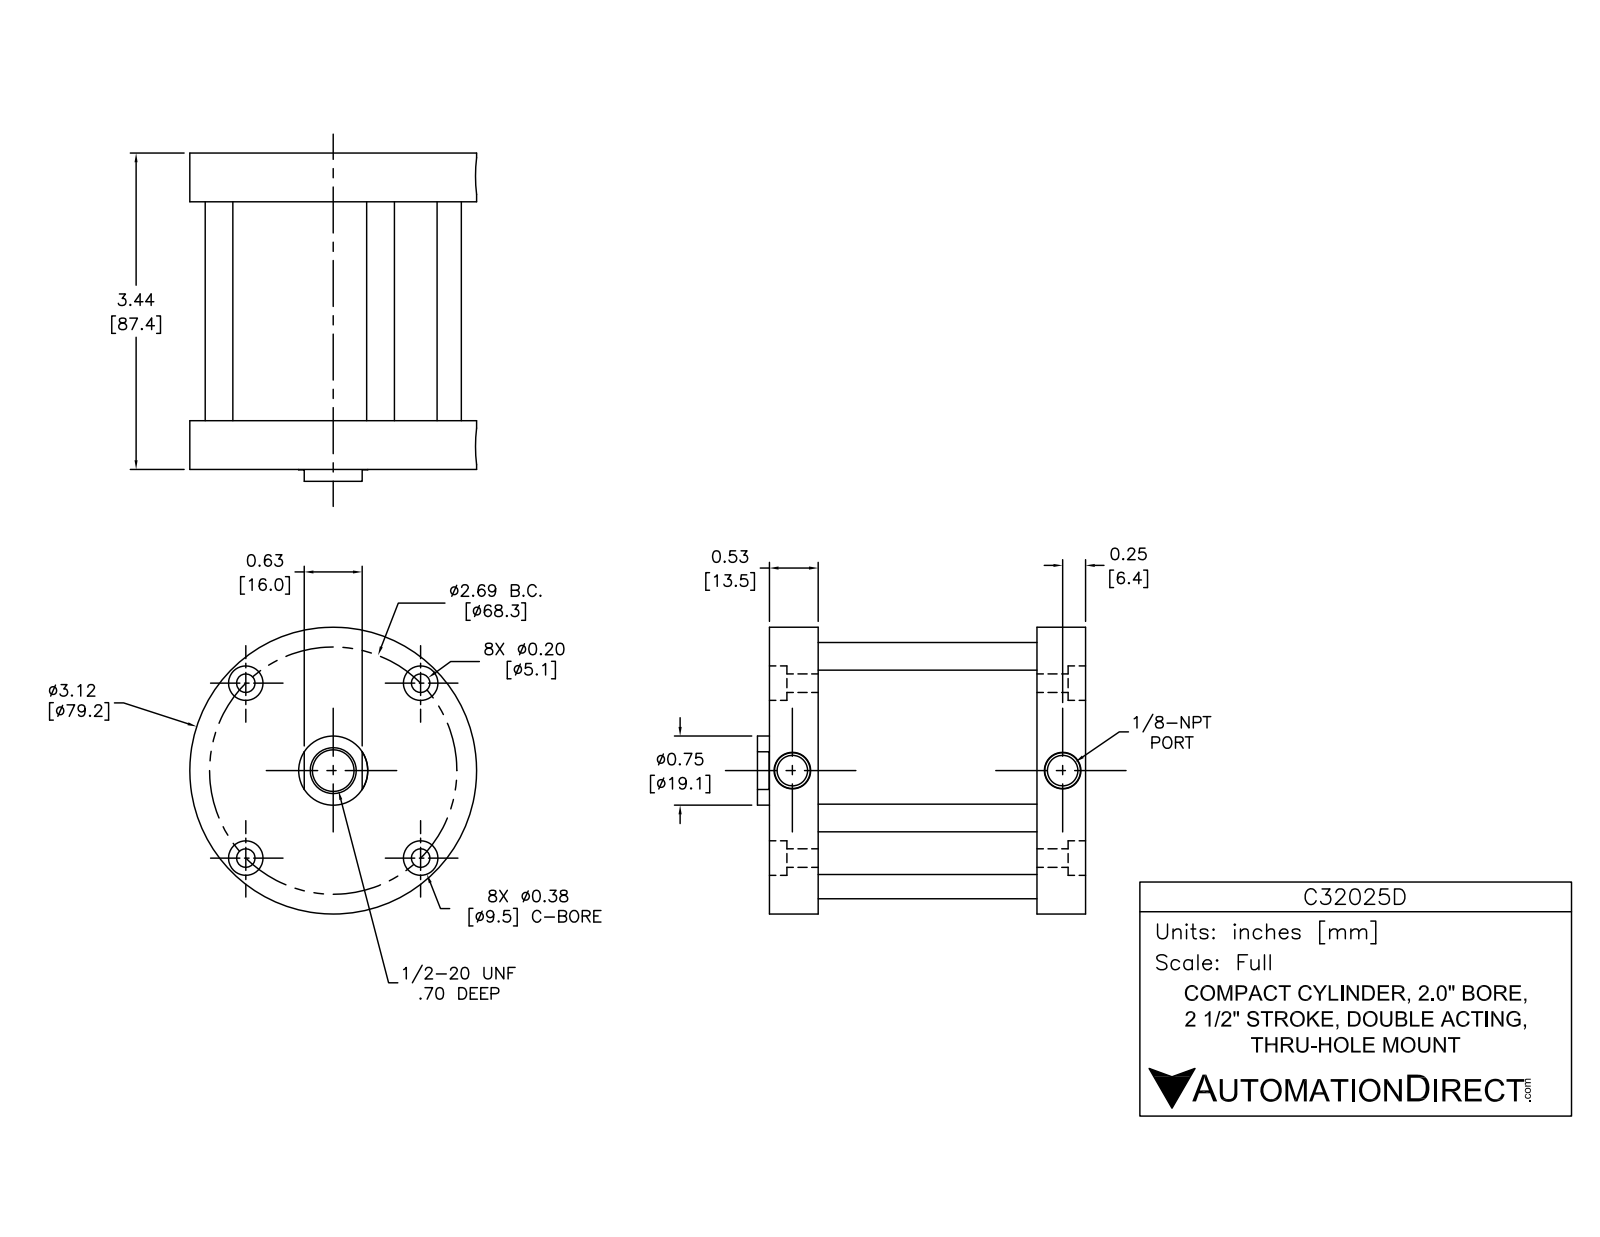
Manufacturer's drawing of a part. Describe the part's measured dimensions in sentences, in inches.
The part is named "C32025D-FO1_BM_r; C32025D-FO1_BM_tube; C32025D-rod_part; C32025D-FO1_BM_heads (+3 more)". Its 3-D file was written by "SolidWorks 2014 (AUTOMOTIVE_DESIGN)". It is 9 solids with 165 faces: 49 planar, 98 cylindrical and 18 other. Overall it measures 3.57 by 3.12 by 3.12 inches. Its volume is 10.1 cubic inches and its surface area 118.7 square inches. Round holes: 4 of diameter 0.2, 4 of diameter 0.218, 4 of diameter 0.343, 2 of diameter 0.125, 1 of diameter 0.446, 1 of diameter 0.75, 1 of diameter 0.752, 1 of diameter 2, 1 of diameter 2.06. Round bosses or shafts: 4 of diameter 0.4, 1 of diameter 3.12. The main face-to-face distances are 2.63, 0.25, 0.28, 3.44, 3.16, 2.91, 2.91, 0.53, 0.53, 2.38. The hole center spacings are 0.432, 1.345, 1.345, 1.572, 1.902, 1.902, 2.183, 2.655.
